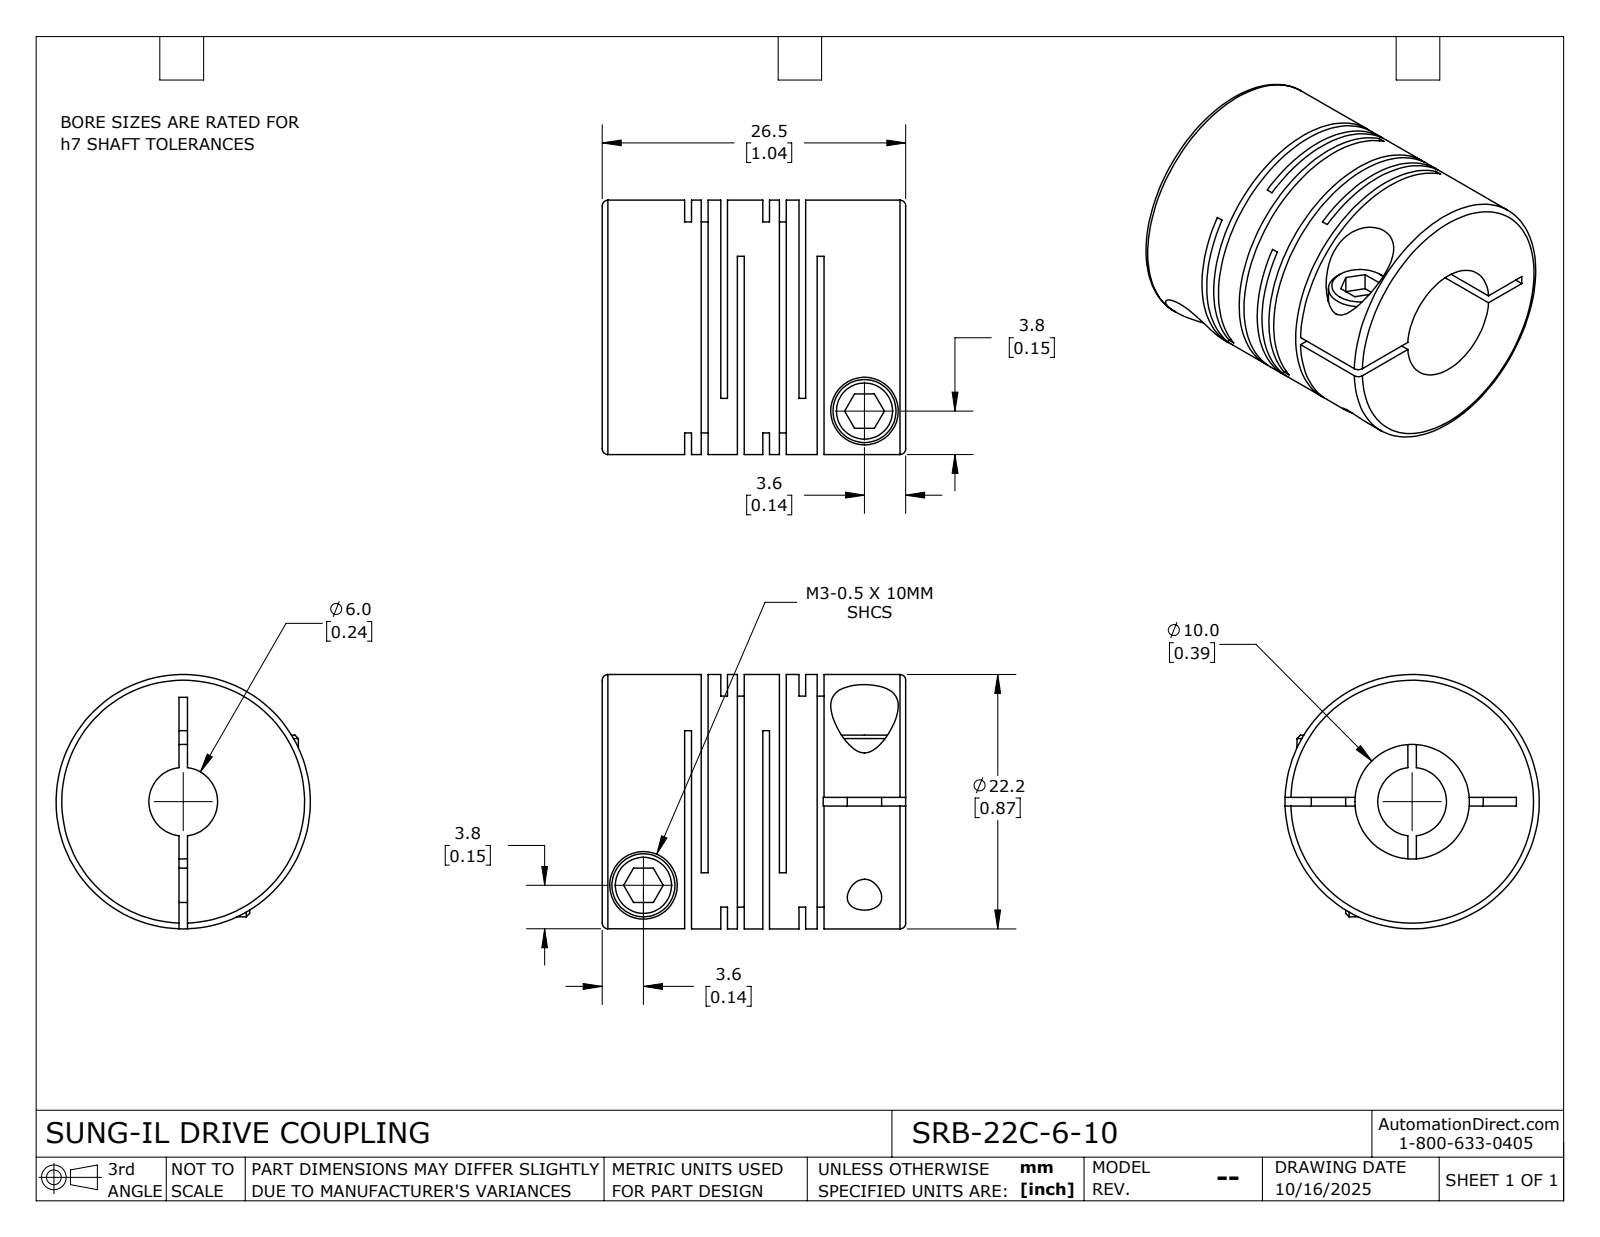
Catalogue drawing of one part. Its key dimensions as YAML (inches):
part_name: "SRB-22C-6-10"
step_written_by: "SolidWorks 2024 (CONFIG_CONTROL_DESIGN)"
units: inches
bodies: {solids: 1, faces: 115, planar: 60, cylindrical: 42, other: 13}
overall_size: [1.043, 0.874, 0.874]
volume: 0.431
surface_area: 11.59
round_holes:
  - {diameter: 0.118, count: 2}
  - {diameter: 0.232, count: 2}
  - {diameter: 0.236, count: 1}
  - {diameter: 0.394, count: 1}
round_bosses_or_shafts:
  - {diameter: 0.217, count: 2}
  - {diameter: 0.874, count: 1}
face_to_face_distances: [0.023, 0.124, 0.269, 0.057, 0.211, 0.144, 0.067, 0.08, 0.147, 0.292]
